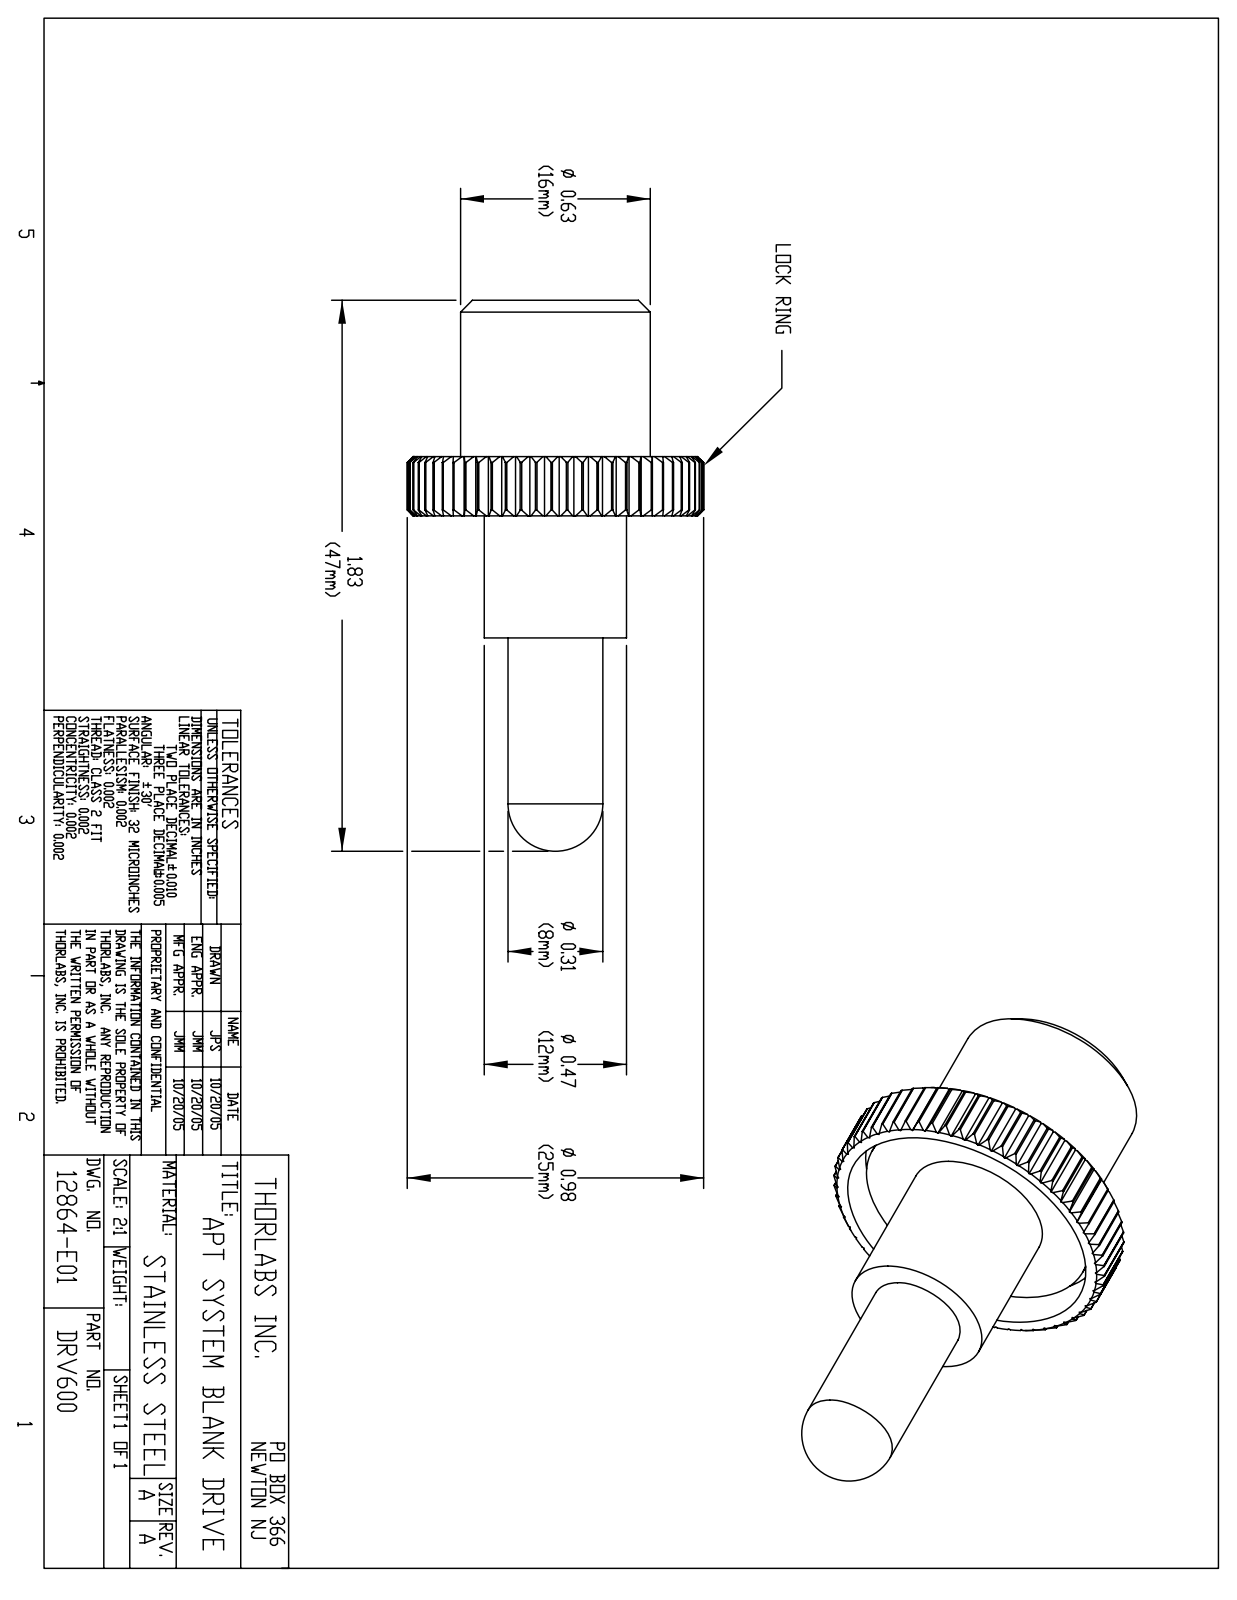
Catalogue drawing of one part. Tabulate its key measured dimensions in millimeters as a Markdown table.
| quantity | value |
| --- | --- |
| part name | 12864-E0W |
| STEP written by | SolidWorks 2007 (AUTOMOTIVE_DESIGN) |
| units | millimeters |
| bodies | 0 solids, 384 faces (190 planar, 70 cylindrical, 124 other) |
| overall size | 46.5 × 25 × 25 |
| round holes (diameter × count) | 18.4 × 1, 22 × 1 |
| round bosses / shafts (diameter × count) | 16 × 1, 12 × 1, 8 × 1 |
| partial cylindrical surfaces (radius × count) | 12.5 × 1 |
| main face-to-face distances | 1.5, 1.3, 2.8, 13.2, 14.5, 16, 16.8, 16.8, 18.2, 5 |
